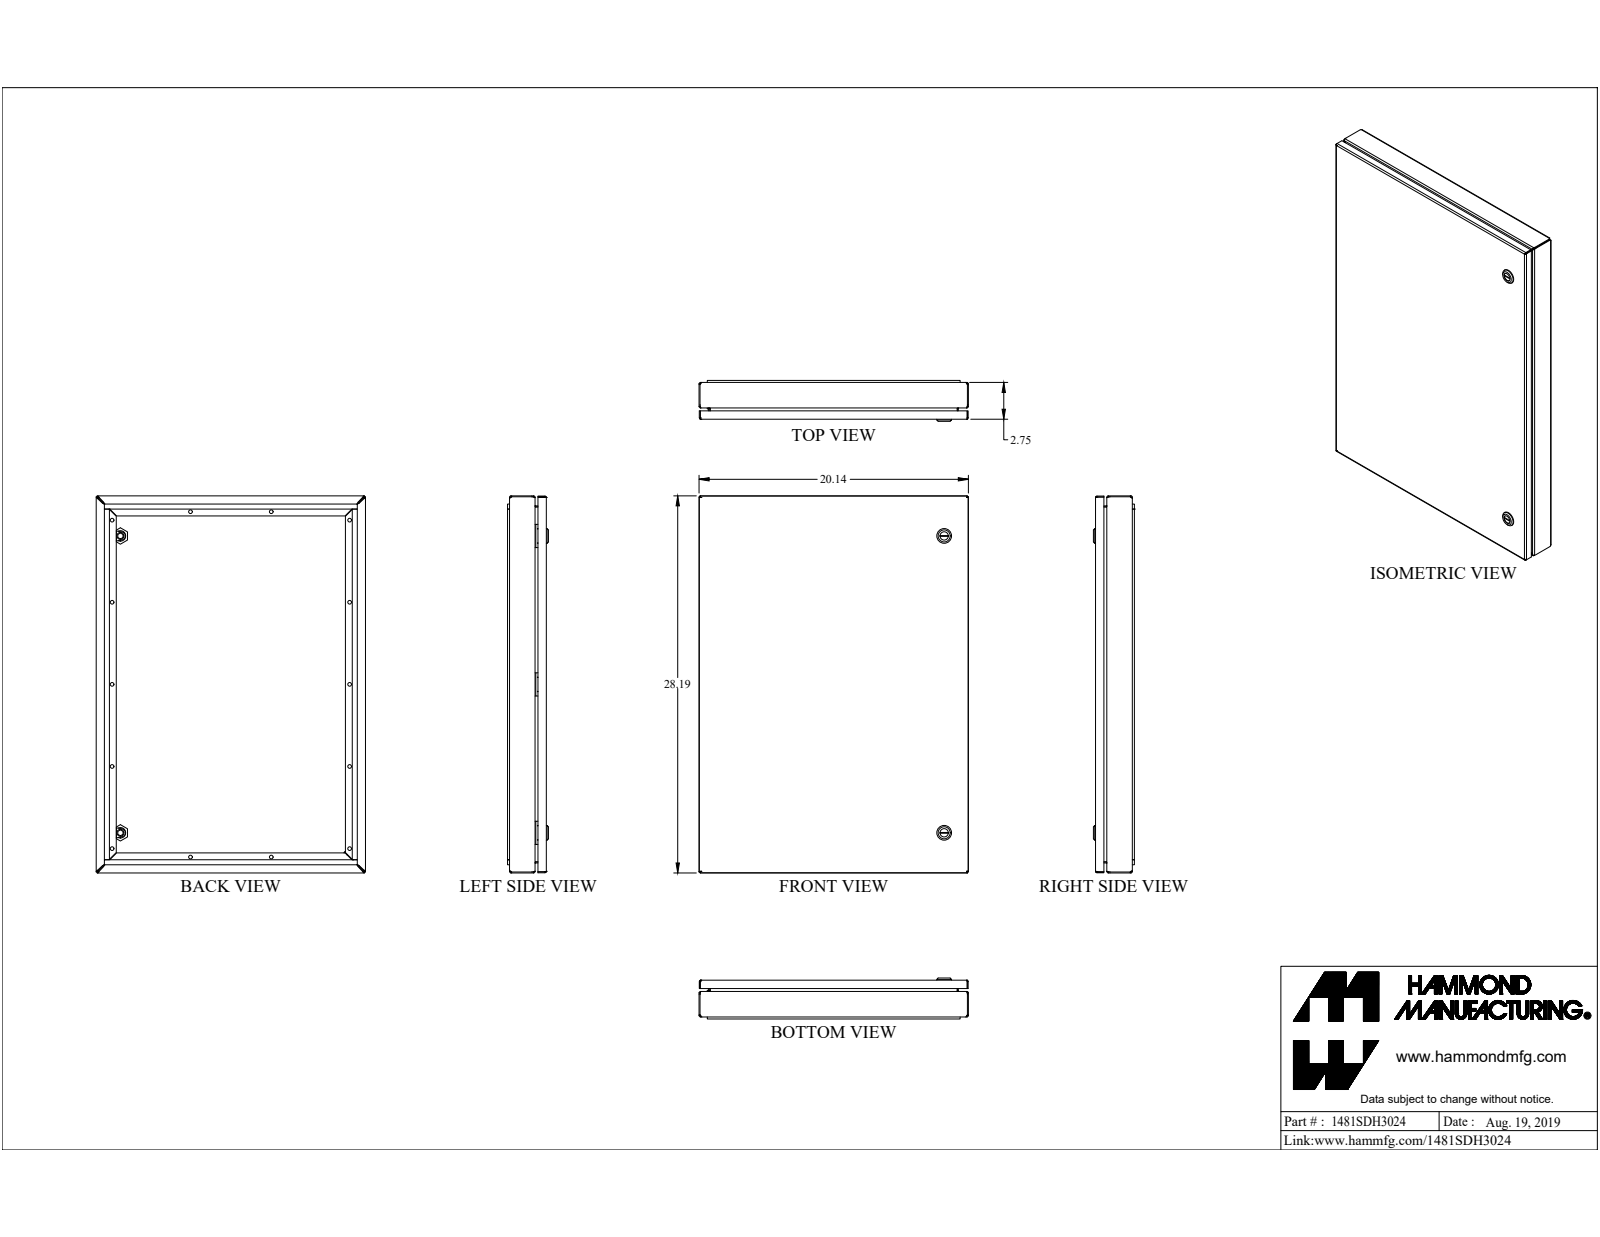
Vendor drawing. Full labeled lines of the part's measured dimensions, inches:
Part name (STEP PRODUCT): 1481SDH3024
STEP written by: SolidWorks 2019 (CONFIG_CONTROL_DESIGN)
Units: inches
Bodies: 31 solids, 776 faces (449 planar, 213 cylindrical, 114 other)
Overall size (bounding box): 28.19 × 20.14 × 3.061
Volume: 95.41 in³ · Surface area: 2 498 in²
Round holes (diameter × count): ⌀0.281 ×14, ⌀0.232 ×2, ⌀0.625 ×2, ⌀0.785 ×2, ⌀0.172 ×1, ⌀0.24 ×1, ⌀0.242 ×1
Round bosses / shafts (diameter × count): ⌀1.1 ×2, ⌀0.525 ×2, ⌀0.455 ×1, ⌀0.398 ×1, ⌀0.356 ×1, ⌀0.313 ×1, ⌀0.292 ×1, ⌀0.25 ×1
Partial cylindrical surfaces — rounded edges, fillets, slot ends (radius × count): R0.036 ×28, R0.108 ×28, R0.382 ×12, R19.003 ×8, R0.006 ×6, R0.062 ×6, R0.125 ×4, R0.25 ×4
Main face-to-face distances: 0.072, 2.579, 0.843, 1.736, 2.651, 20.068, 2.507, 2.679, 1.836, 0.1
Hole centre spacings: 6.137, 18.794, 12.274, 21.592, 17.764, 5.893, 11.922, 18.411
